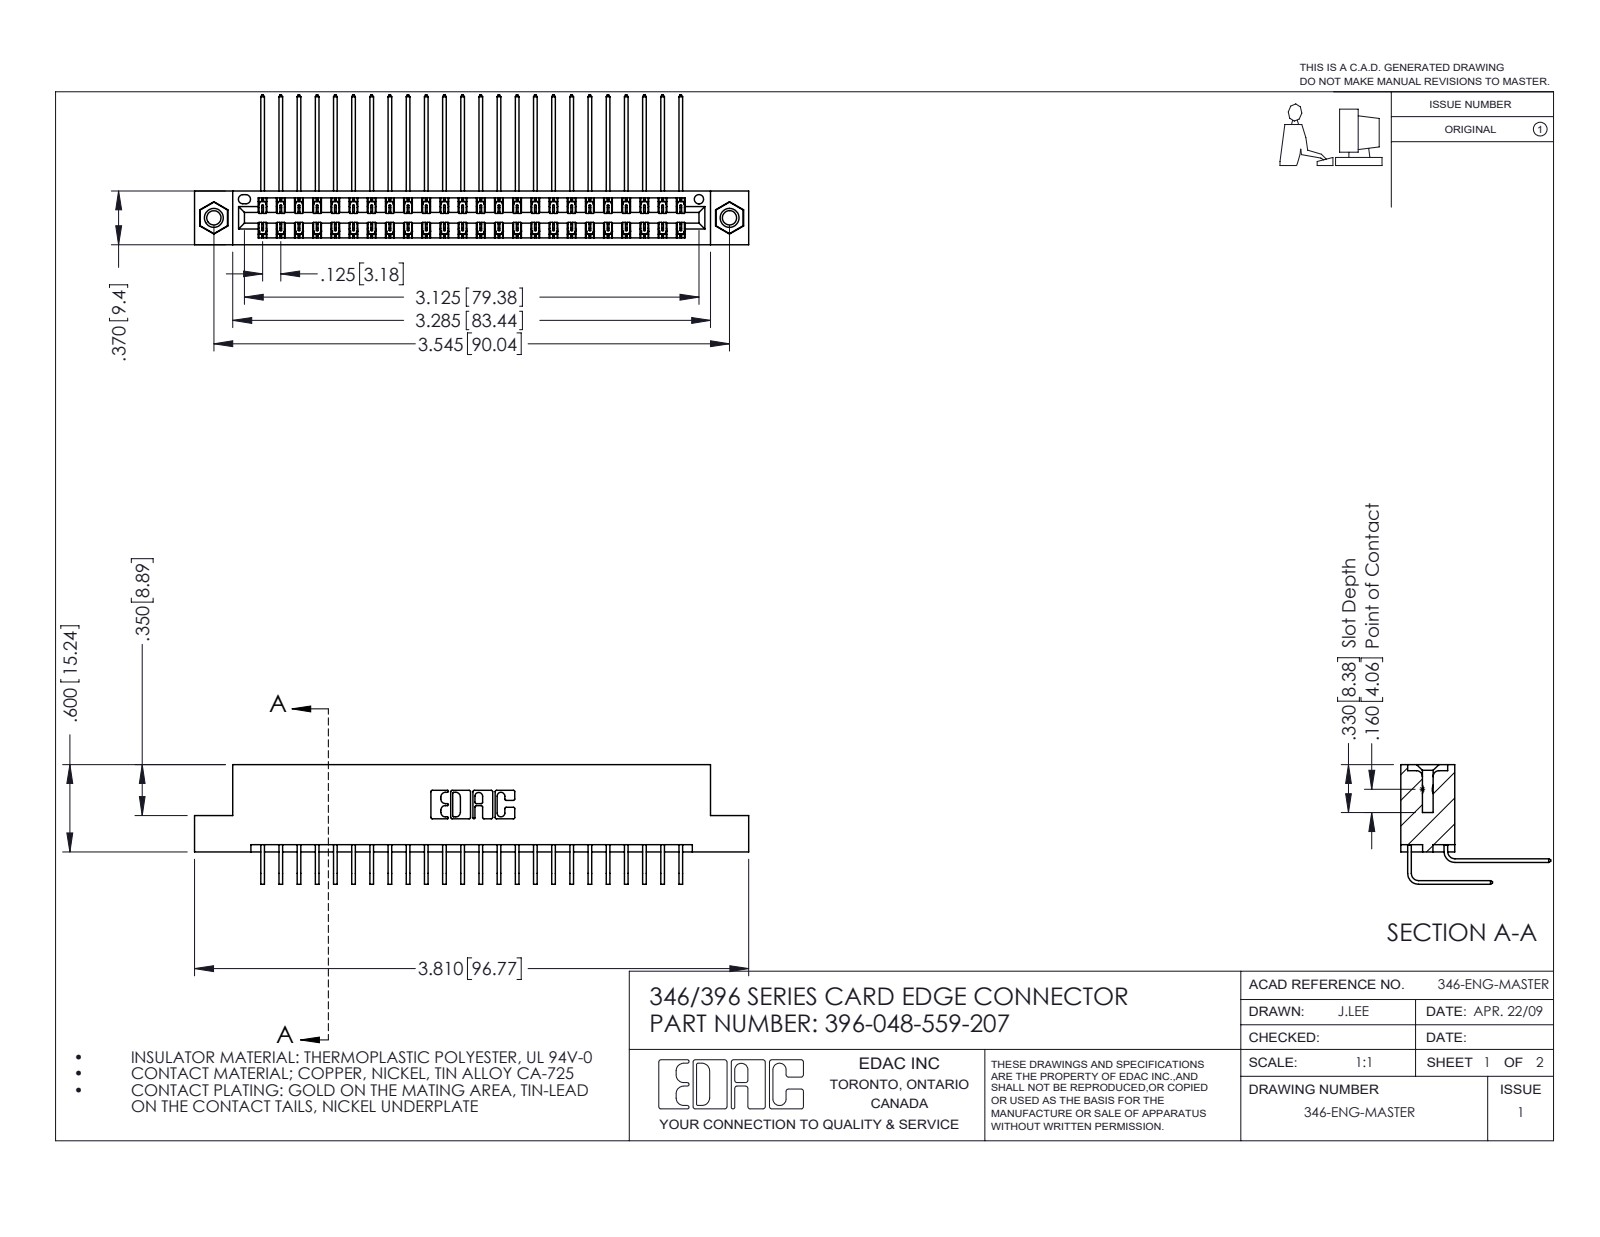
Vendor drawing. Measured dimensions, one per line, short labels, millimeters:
name: 396-048-559-207; 345-250-001_345-250-005-103; 345-292-001_559 Tail - 2; 345-292-001_558 559 Tail - 1 (+1 more)
written by: SolidWorks 2016 (CONFIG_CONTROL_DESIGN)
unit: mm
bodies: 51 solids, 2774 faces (1884 planar, 874 cylindrical, 16 other)
size: 96.8 × 26.2 × 20.9
volume: 9 550 mm³; area: 14 220 mm²
holes: 2× ⌀2.5, 2× ⌀3.2, 2× ⌀4, 1× ⌀1.6
bosses: 2× ⌀3.9
rounds: 72× R0.2, 22× R0.3, 6× R0.2, 6× R0.8, 3× R0.7, 2× R0.4, 2× R0.6, 2× R0.6
face distances: 1.2, 8.2, 0.6, 6.4, 9.4, 1.8, 7.6, 7, 3.8, 5.6
hole spacings: 6.2, 84.8, 90
